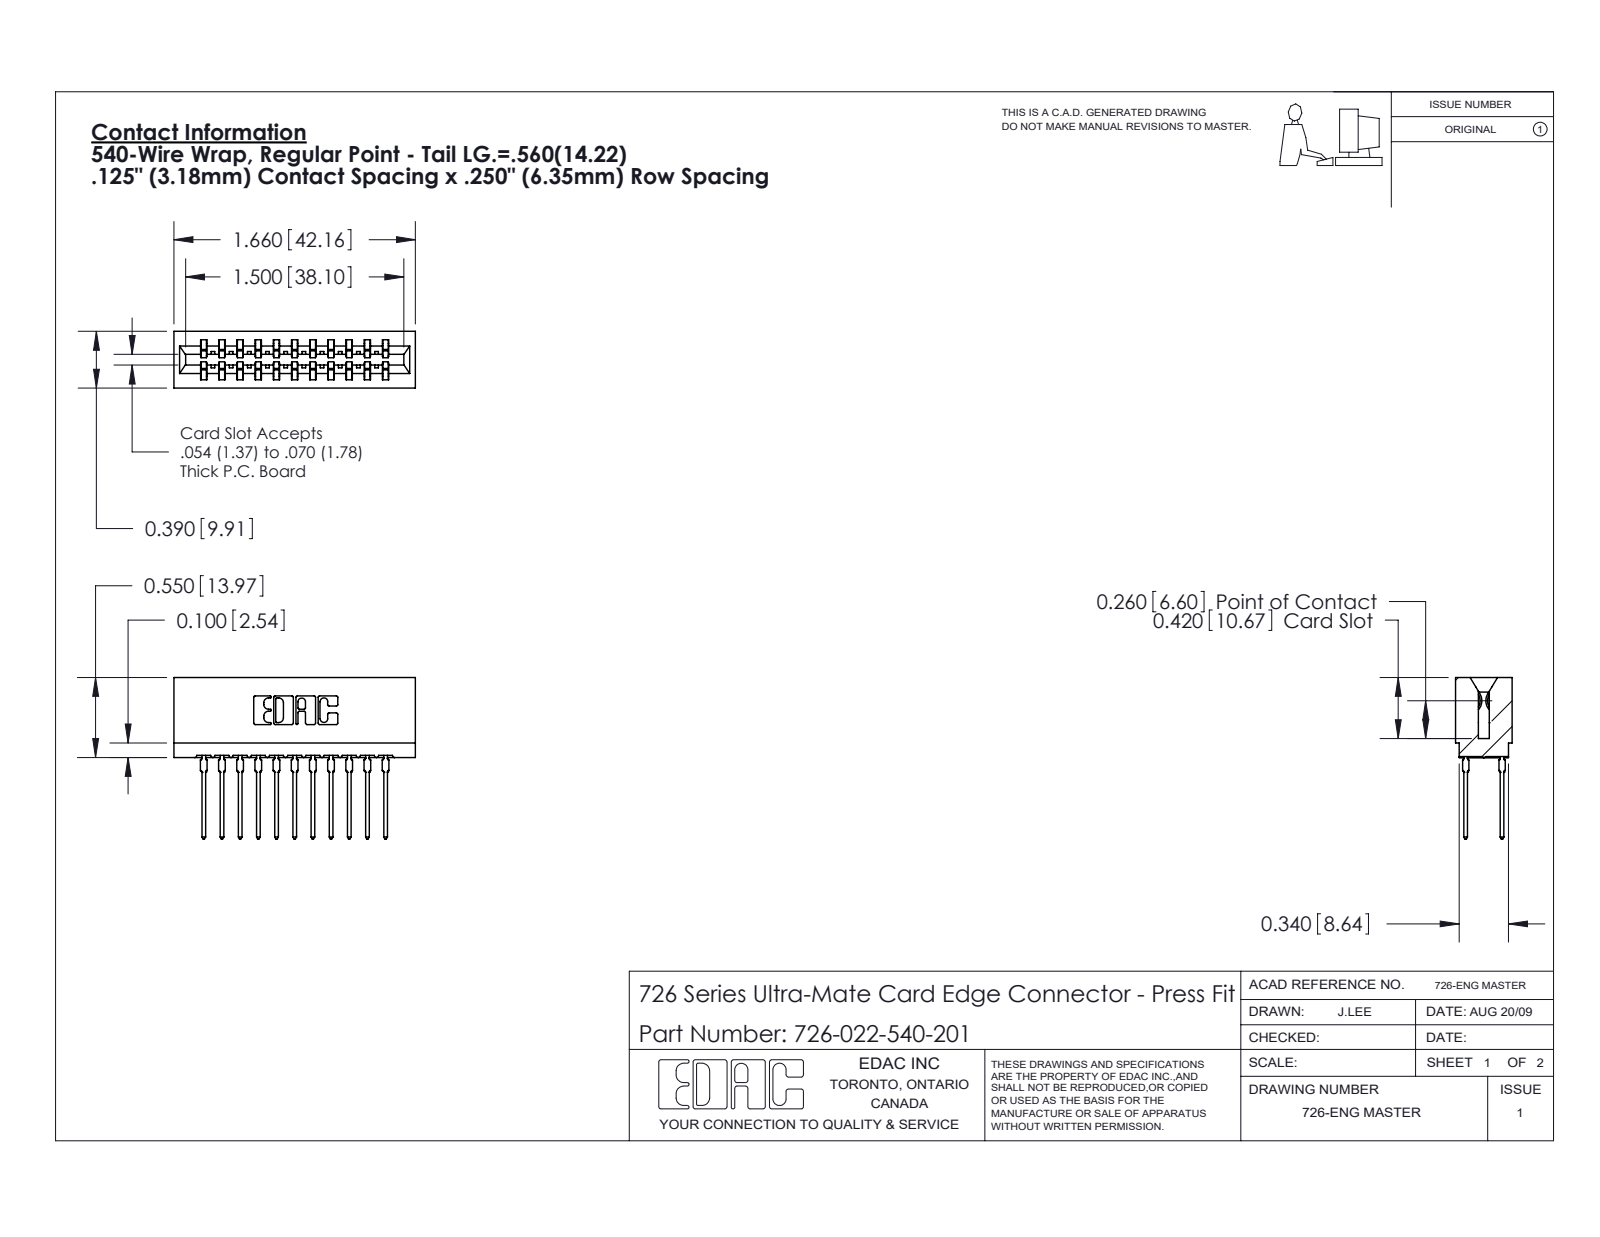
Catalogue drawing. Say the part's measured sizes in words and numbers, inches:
The part is named "726-022-540-201; 746-292-001_540; 726 Part_.515 Slot Depth - 01". Its 3-D file was written by "SolidWorks 2020 (CONFIG_CONTROL_DESIGN)". It is 23 solids with 2066 faces: 1067 planar, 427 cylindrical and 572 other. Overall it measures 1.66 by 1.109 by 0.39 inches. Its volume is 0.251 cubic inches and its surface area 10.24 square inches. Partial cylindrical surfaces (rounded edges, fillets, slot ends): 44 of radius 0.021, 22 of radius 0.01, 12 of radius 0.015, 8 of radius 0.005, 8 of radius 0.011, 6 of radius 0.007, 6 of radius 0.031, 3 of radius 0.026. The main face-to-face distances are 0.25, 0.333, 0.057, 0.083, 0.025, 0.5, 0.75, 0.042, 0.307, 0.125.
